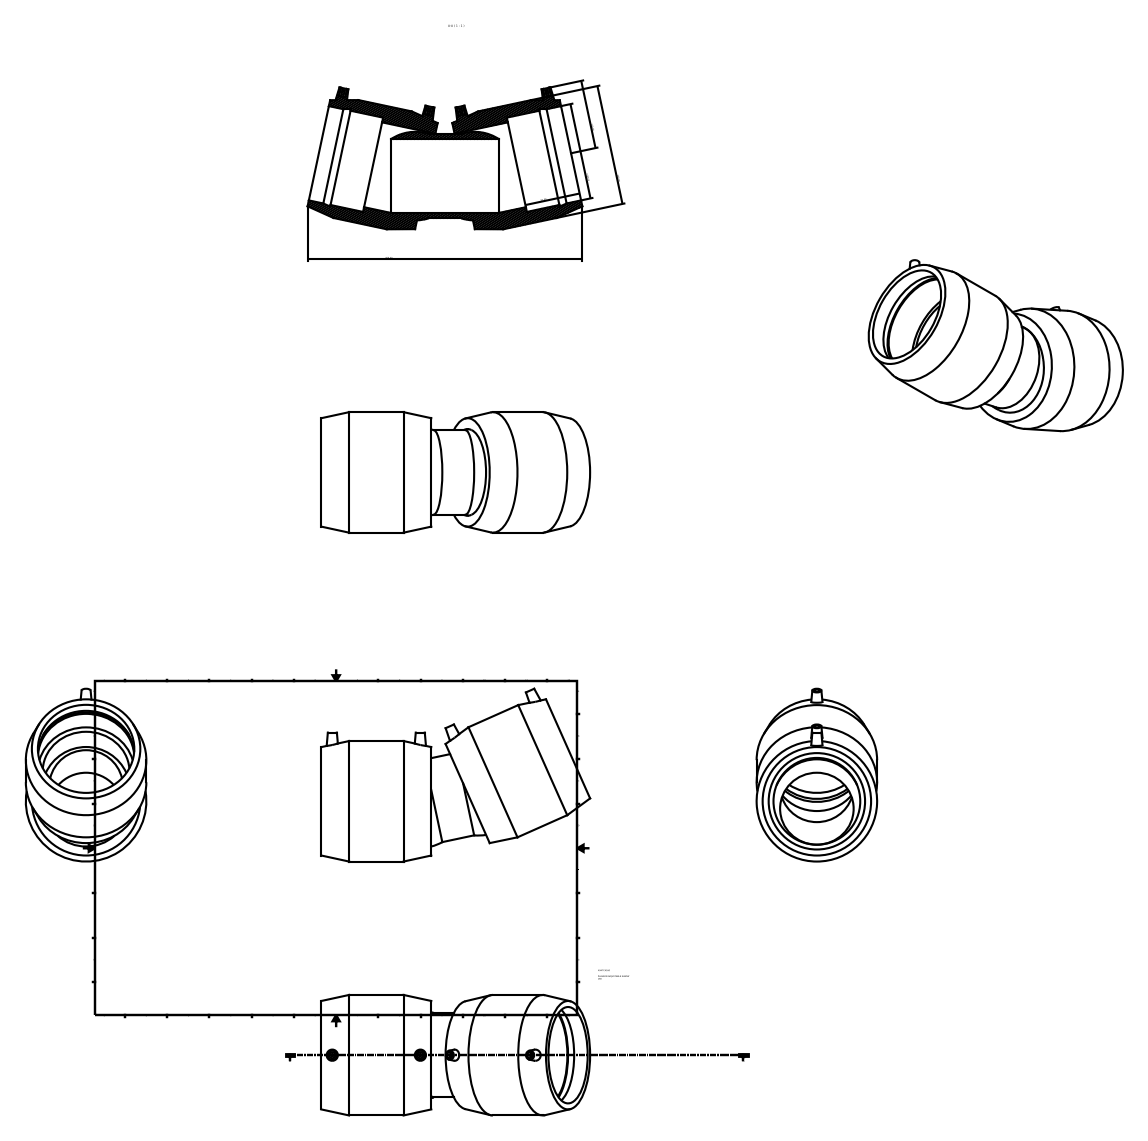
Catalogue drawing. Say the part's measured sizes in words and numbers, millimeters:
The part is named "4947C4160". Its 3-D file was written by "Autodesk Inventor 2015 (AUTOMOTIVE_DESIGN)". It is 1 solid with 50 faces: 20 planar, 18 cylindrical and 12 other. Overall it measures 446.04 by 286.8 by 200 millimeters. Its volume is 4 896 000 cubic millimeters and its surface area 554 660 square millimeters. Round holes: 4 of diameter 10, 3 of diameter 160, 2 of diameter 144, 1 of diameter 122.06. Round bosses or shafts: 4 of diameter 4, 2 of diameter 200, 1 of diameter 140.14. The main face-to-face distances are 182.4, 182.5, 92, 90.4, 90.45, 92.05, 36.8, 55.2, 145.6, 145.68. The hole center spacings are 145.92.
